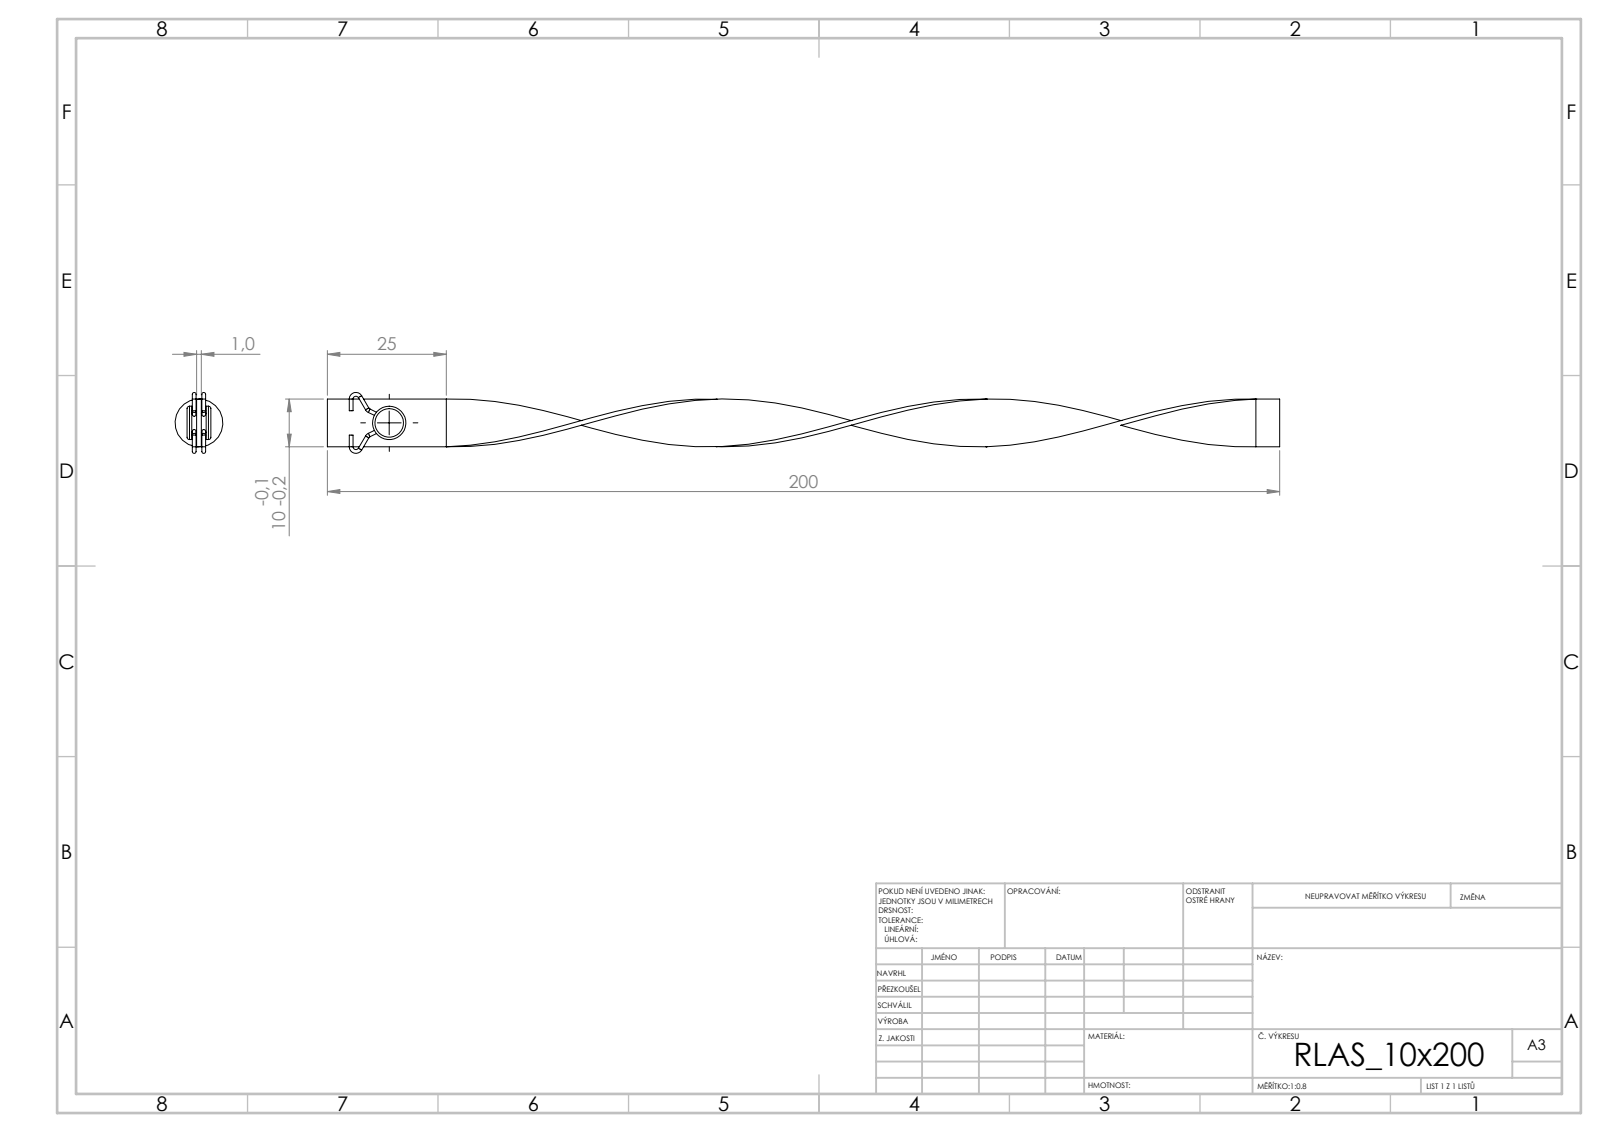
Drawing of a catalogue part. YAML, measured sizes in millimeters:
step_written_by: "SolidWorks 2019 (CONFIG_CONTROL_DESIGN)"
units: millimeters
bodies: {solids: 3, faces: 90, planar: 18, cylindrical: 40, other: 32}
overall_size: [200, 12.8, 10.05]
volume: 2135
surface_area: 4801
round_bosses_or_shafts:
  - {diameter: 0.8, count: 14}
  - {diameter: 7, count: 1}
  - {diameter: 4, count: 1}
face_to_face_distances: [1, 2, 3, 4, 10, 5, 200, 2.45, 7.55, 5.1]
